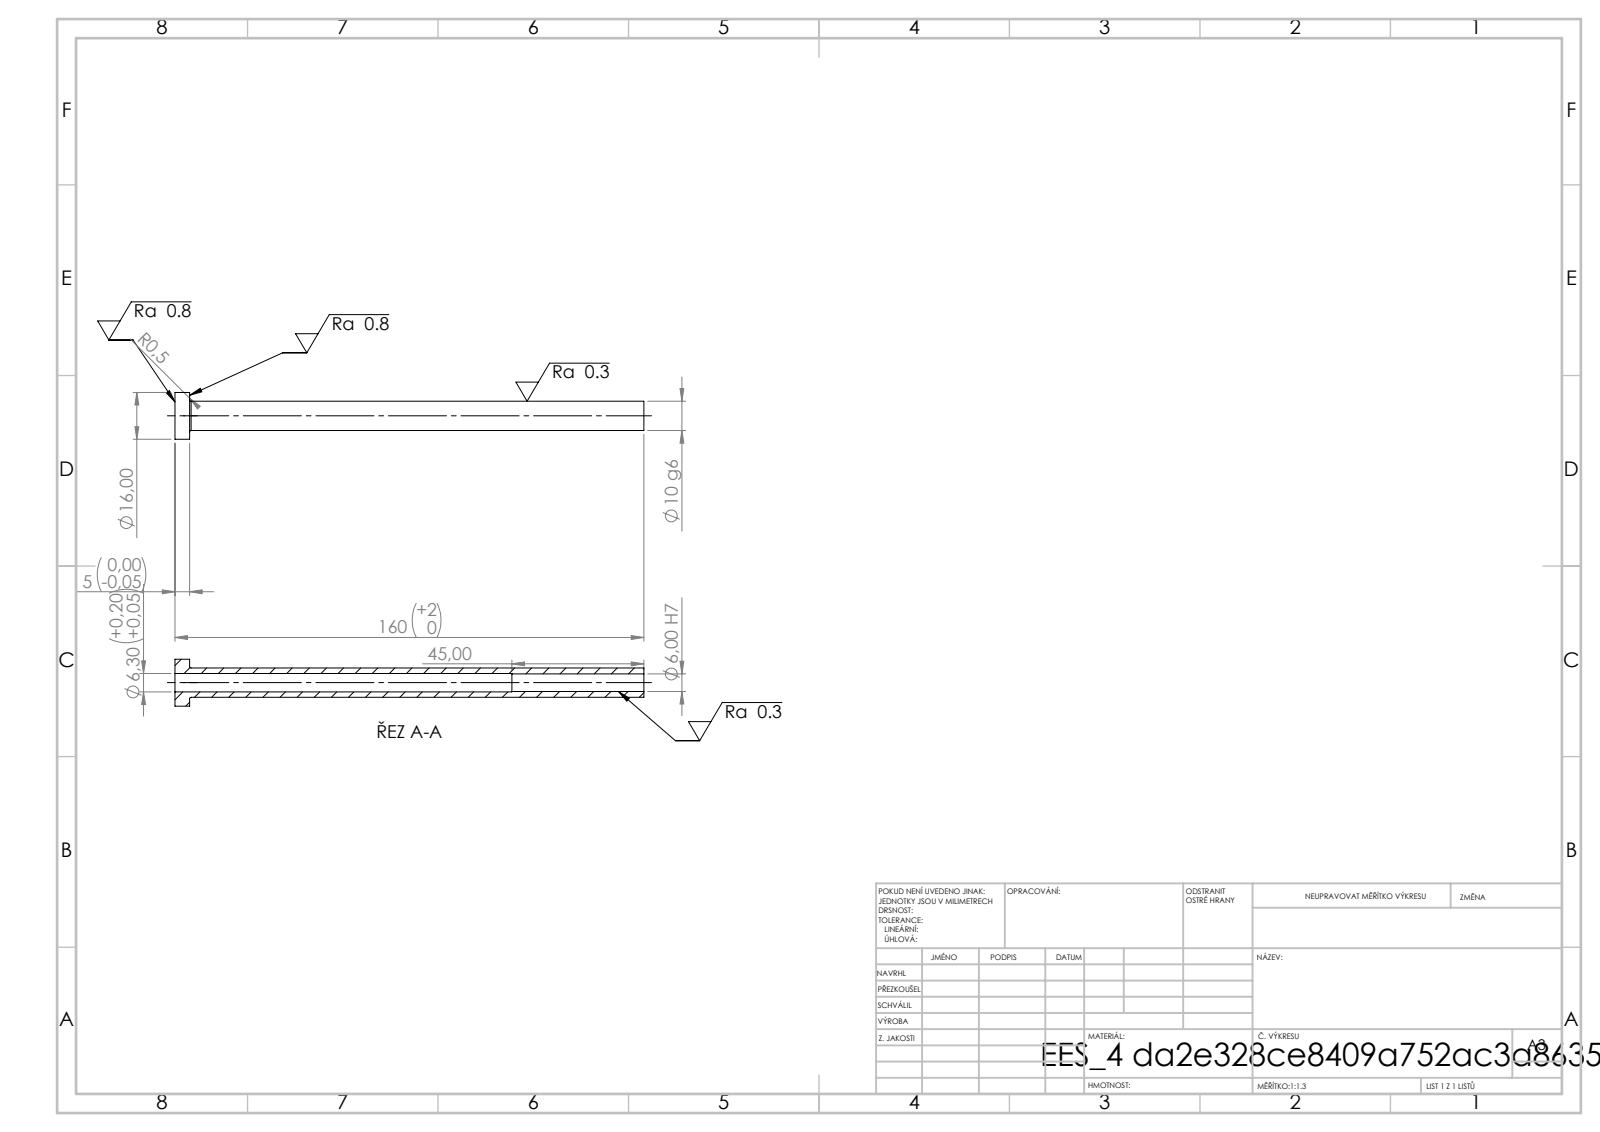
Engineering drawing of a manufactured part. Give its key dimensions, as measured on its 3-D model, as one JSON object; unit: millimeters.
{"step_written_by": "SolidWorks 2019 (CONFIG_CONTROL_DESIGN)", "units": "millimeters", "bodies": {"solids": 1, "faces": 14, "planar": 4, "cylindrical": 8, "other": 2}, "overall_size": [160, 16, 16], "volume_mm3": 8324, "surface_area_mm2": 8584, "round_holes": [[6, 1], [6.3, 1]], "round_bosses_or_shafts": [[16, 1], [10, 1]], "face_to_face_distances": [5, 160, 155, 115, 110, 45]}
